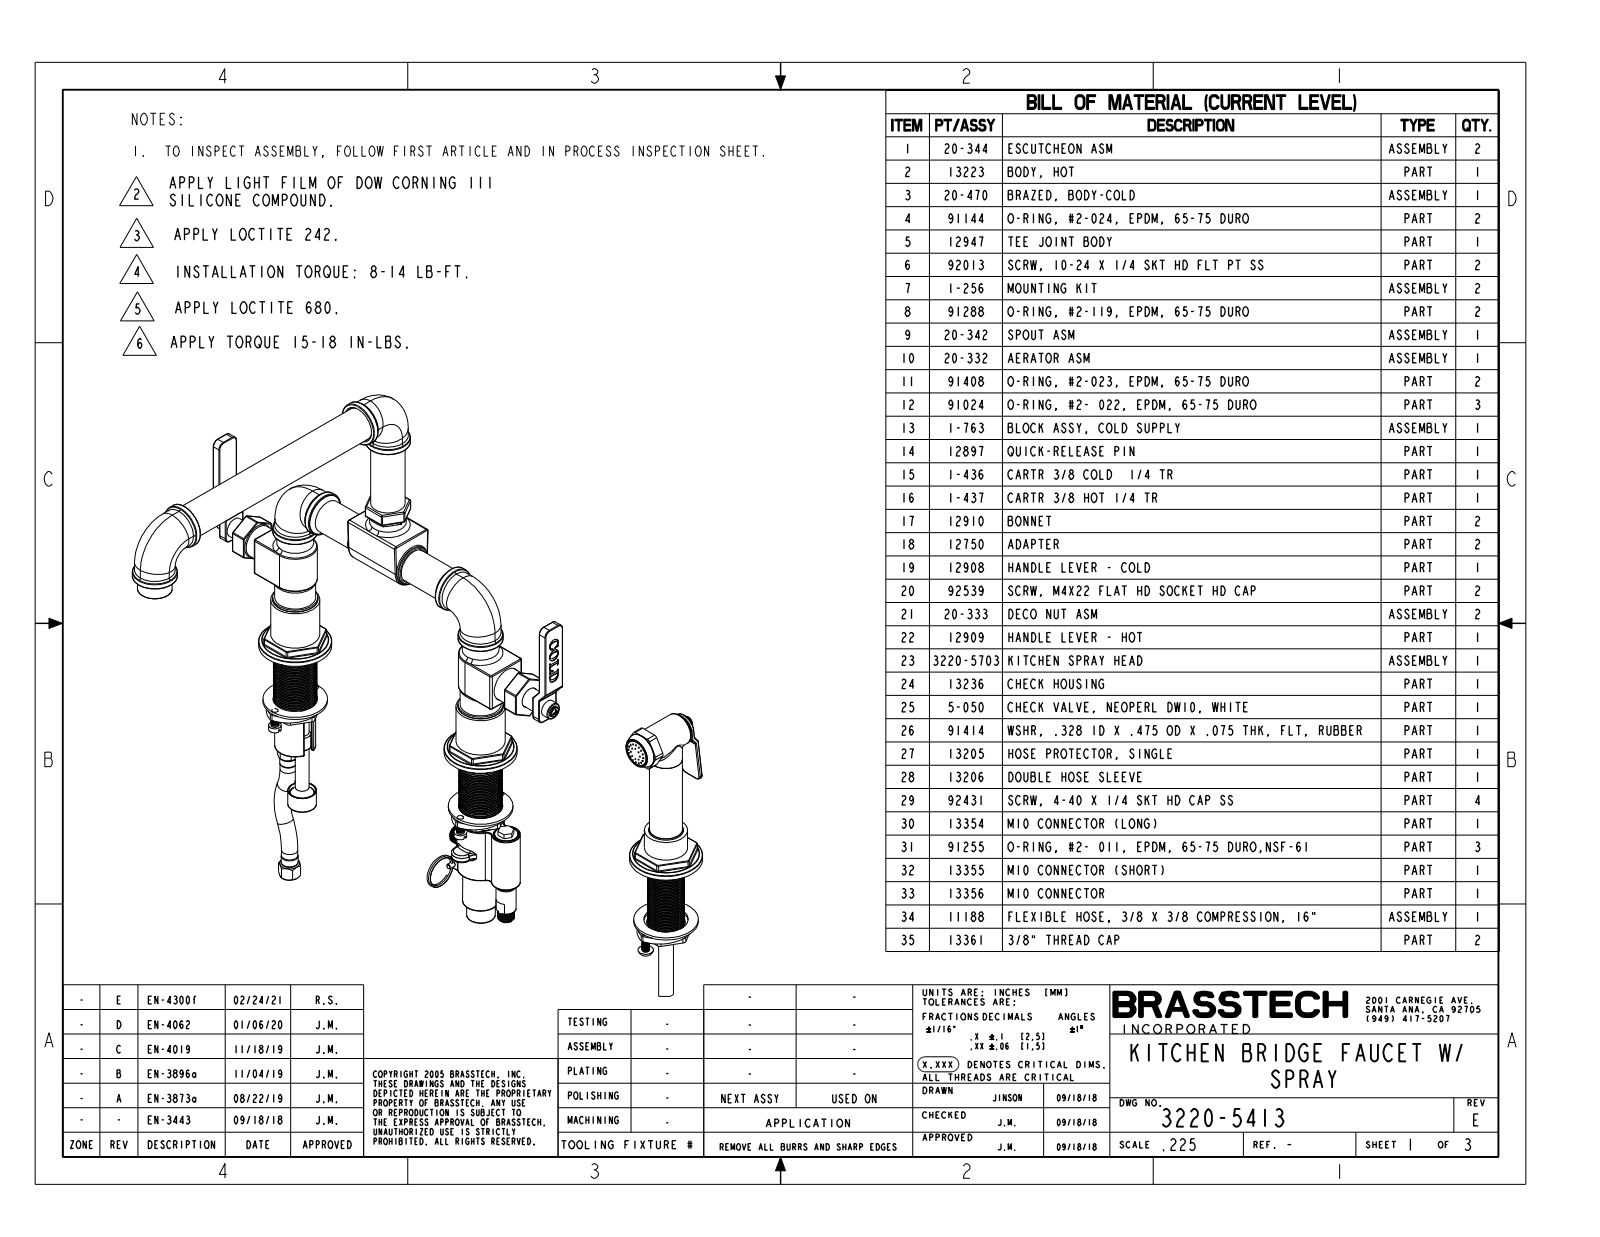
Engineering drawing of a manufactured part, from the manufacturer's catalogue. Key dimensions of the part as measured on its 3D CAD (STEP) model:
Part name (STEP PRODUCT): 3220-5413
STEP written by: CREO PARAMETRIC BY PTC INC, 2018400 (AUTOMOTIVE_DESIGN)
Units: inches
Bodies: 3 solids, 1379 faces (315 planar, 392 cylindrical, 672 other)
Overall size (bounding box): 20.379 × 11.948 × 11.585
Volume: 54.38 in³ · Surface area: 228.1 in²
Round holes (diameter × count): ⌀0.06 ×1, ⌀0.18 ×1, ⌀0.622 ×1, ⌀0.95 ×1
Round bosses / shafts (diameter × count): ⌀1.375 ×6, ⌀2.23 ×3, ⌀1.25 ×3, ⌀1.125 ×3, ⌀1.06 ×3, ⌀1.5 ×2, ⌀1.05 ×2, ⌀1.313 ×1
Partial cylindrical surfaces — rounded edges, fillets, slot ends (radius × count): R0.02 ×84, R0.01 ×61, R0.06 ×40, R0.03 ×29, R0.04 ×24, R0.1 ×6, R0.07 ×5, R0.187 ×4
Main face-to-face distances: 0.425, 0.3, 1.05, 0.275, 14.067, 1.35, 13.792, 9.61, 9.185, 1.2
Hole centre spacings: 1.583
